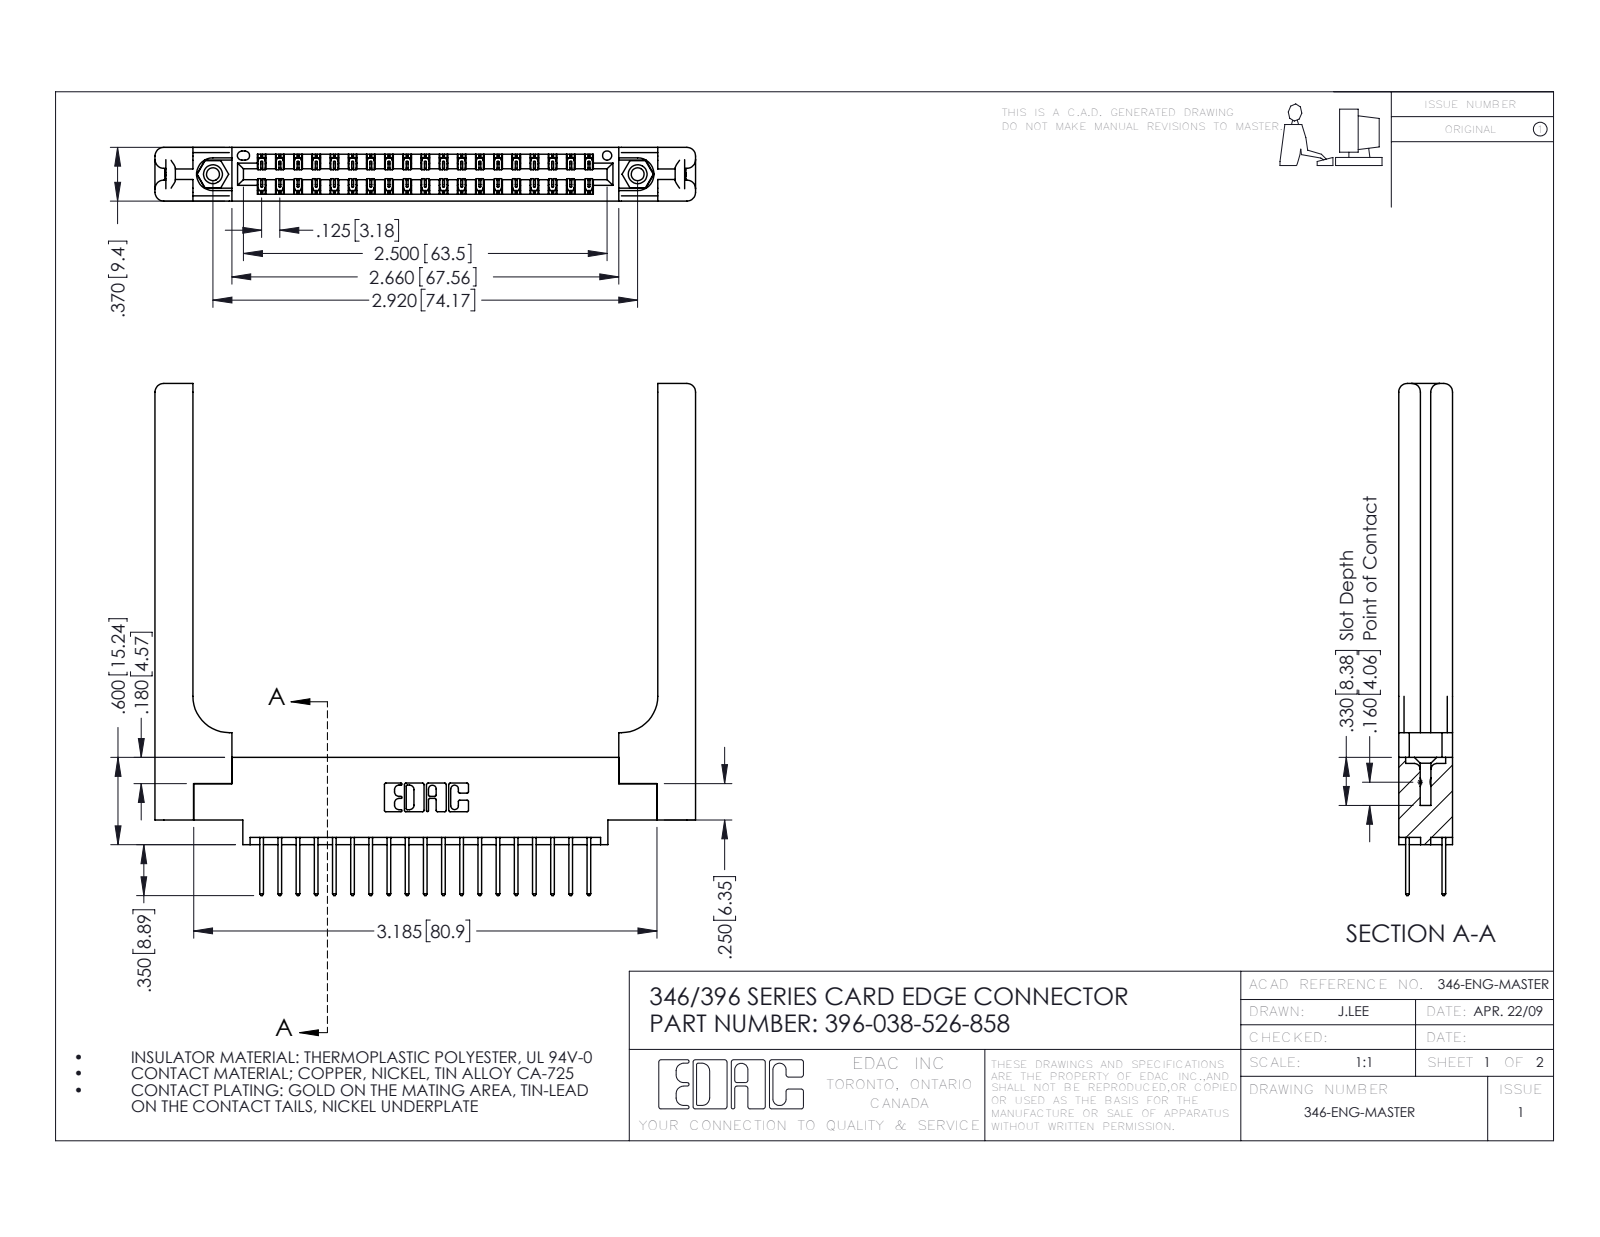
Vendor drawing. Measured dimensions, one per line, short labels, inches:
name: 345-292-001_345-293-126; 345-250-001_345-250-001-102; 396-038-526-858; 346-220-058_345-220-058 (+1 more)
written by: SolidWorks 2016 (CONFIG_CONTROL_DESIGN)
unit: in
bodies: 43 solids, 2358 faces (1558 planar, 740 cylindrical, 60 other)
size: 3.716 × 3.52 × 0.37
volume: 1.002 in³; area: 26.89 in²
holes: 2× ⌀0.089, 2× ⌀0.125, 2× ⌀0.156, 1× ⌀0.064
bosses: 2× ⌀0.155
rounds: 57× R0.006, 38× R0.01, 22× R0.01, 16× R0.06, 6× R0.007, 6× R0.031, 3× R0.026, 2× R0.014
face distances: 0.37, 0.072, 0.048, 0.322, 0.148, 0.15, 0.25, 0.025, 0.298, 0.077
hole spacings: 0.246, 2.713, 2.92
